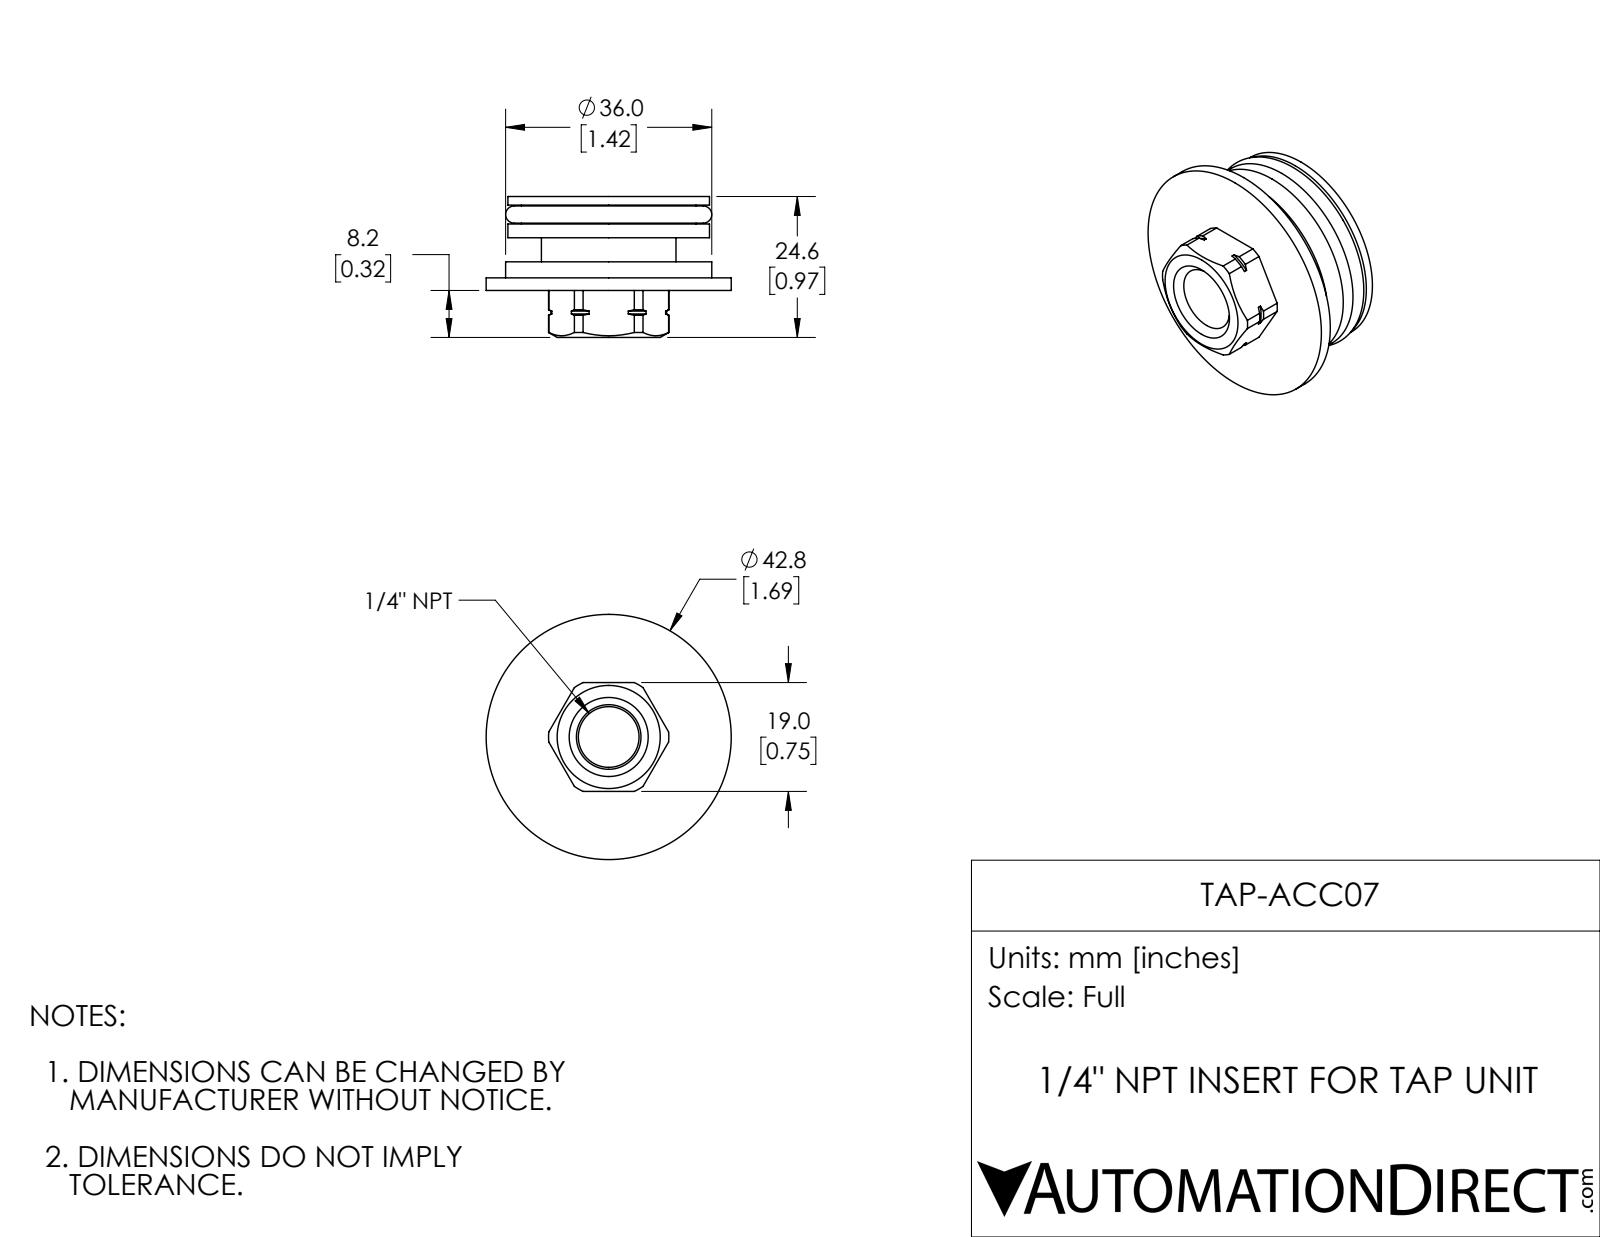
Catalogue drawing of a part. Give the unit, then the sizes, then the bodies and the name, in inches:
Units: inches
Overall size (bounding box): 1.685 × 1.685 × 0.969
Round holes (diameter × count): ⌀0.417 ×1, ⌀1.024 ×1
Round bosses / shafts (diameter × count): ⌀1.685 ×1, ⌀1.417 ×1, ⌀1.386 ×1, ⌀1.201 ×1, ⌀0.925 ×1
Partial cylindrical surfaces — rounded edges, fillets, slot ends (radius × count): R0.398 ×1, R0.413 ×1
Main face-to-face distances: 0.197, 0.362, 0.165, 0.646, 0.449, 0.283, 0.087, 0.11, 0.276, 0.559
Volume: 0.771 in³ · Surface area: 12.27 in²
Bodies: 1 solid, 74 faces (14 planar, 36 cylindrical, 24 other)
Part name (STEP PRODUCT): TAP-ACC07
STEP written by: SolidWorks 2017 (AUTOMOTIVE_DESIGN)
